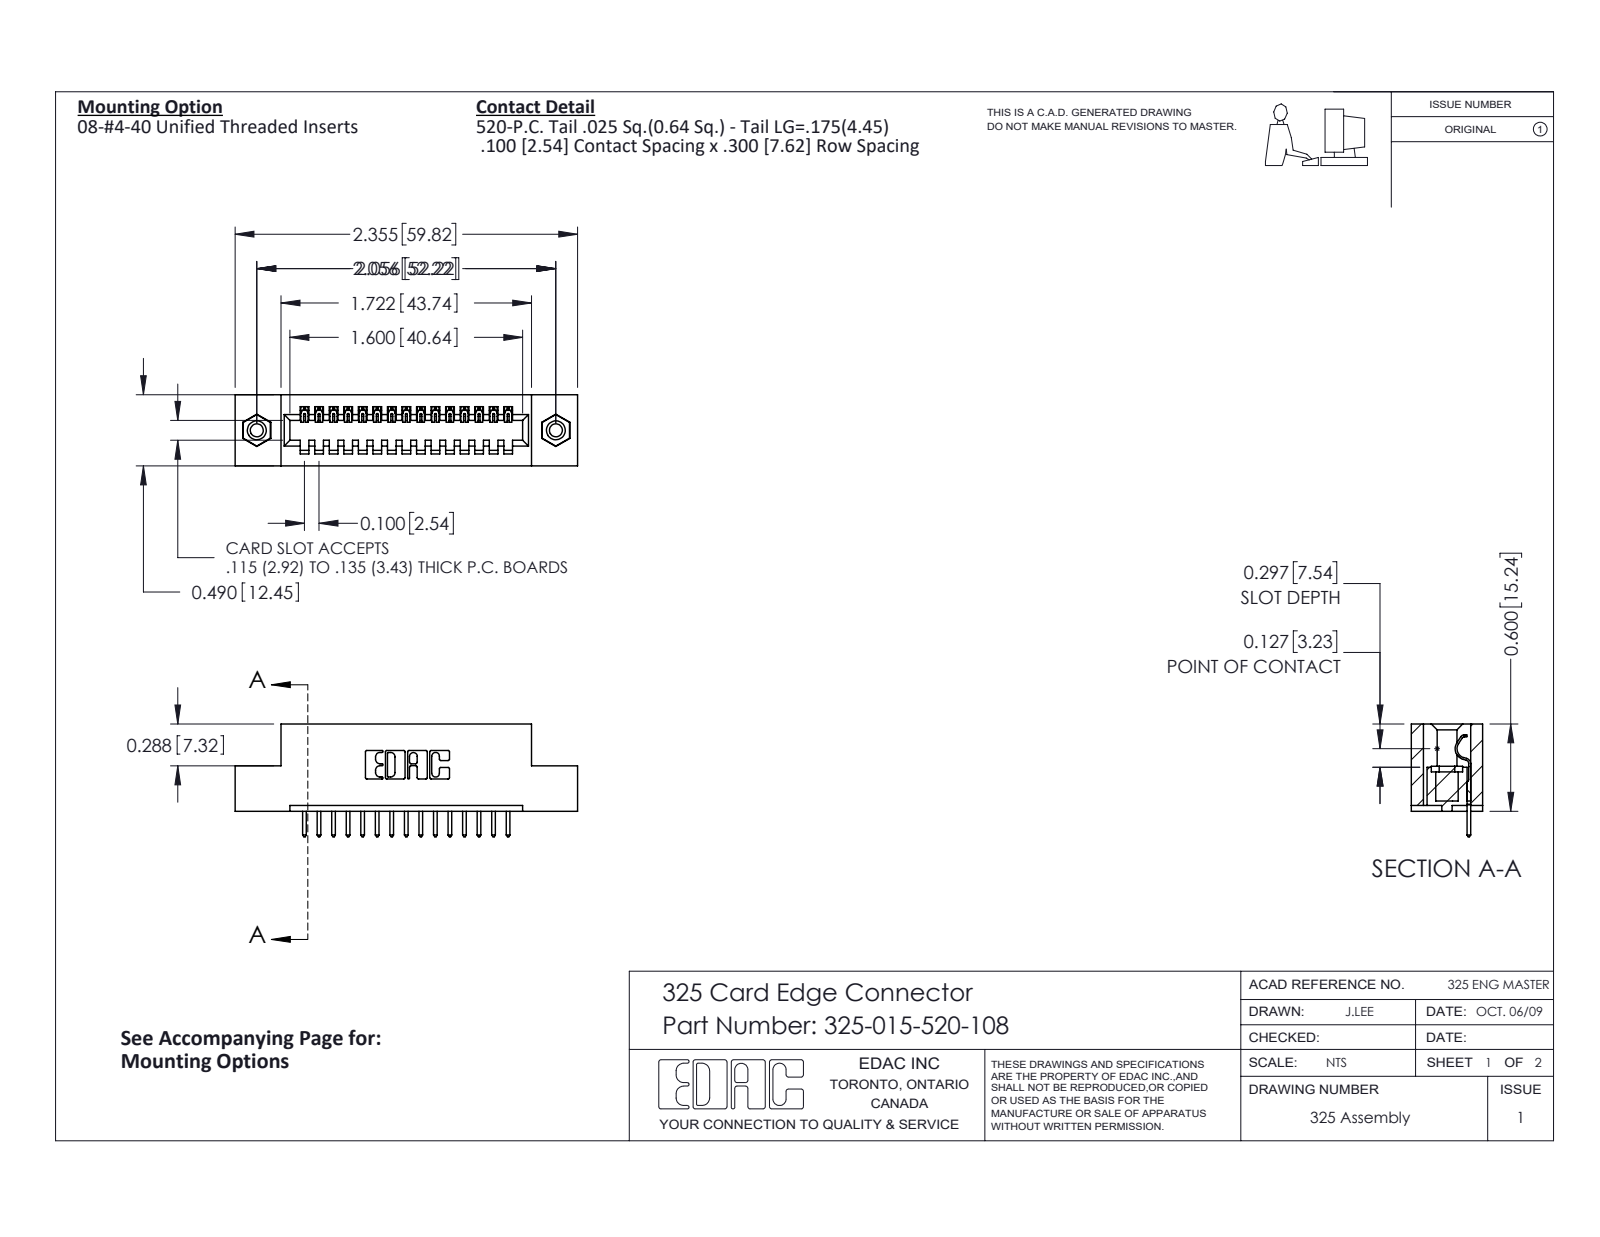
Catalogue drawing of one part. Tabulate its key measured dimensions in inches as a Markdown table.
| quantity | value |
| --- | --- |
| part name | 325-015-520-108; 345-250-001_345-250-003-102; 325-292-001_325-293-120; 325 Part_TI |
| STEP written by | SolidWorks 2016 (CONFIG_CONTROL_DESIGN) |
| units | inches |
| bodies | 18 solids, 1044 faces (732 planar, 296 cylindrical, 16 other) |
| overall size | 2.355 × 0.775 × 0.49 |
| volume | 0.448 in³ |
| surface area | 11.49 in² |
| round holes (diameter × count) | 0.089 × 2, 0.125 × 2, 0.16 × 2 |
| round bosses / shafts (diameter × count) | 0.155 × 2 |
| partial cylindrical surfaces (radius × count) | 0.006 × 30, 0.01 × 30, 0.01 × 22, 0.007 × 6, 0.031 × 6, 0.026 × 3, 0.014 × 1, 0.022 × 1 |
| main face-to-face distances | 0.083, 0.407, 0.49, 0.3, 0.04, 0.1, 0.107, 0.383, 0.025, 0.6 |
| hole center spacings | 2.056 |
